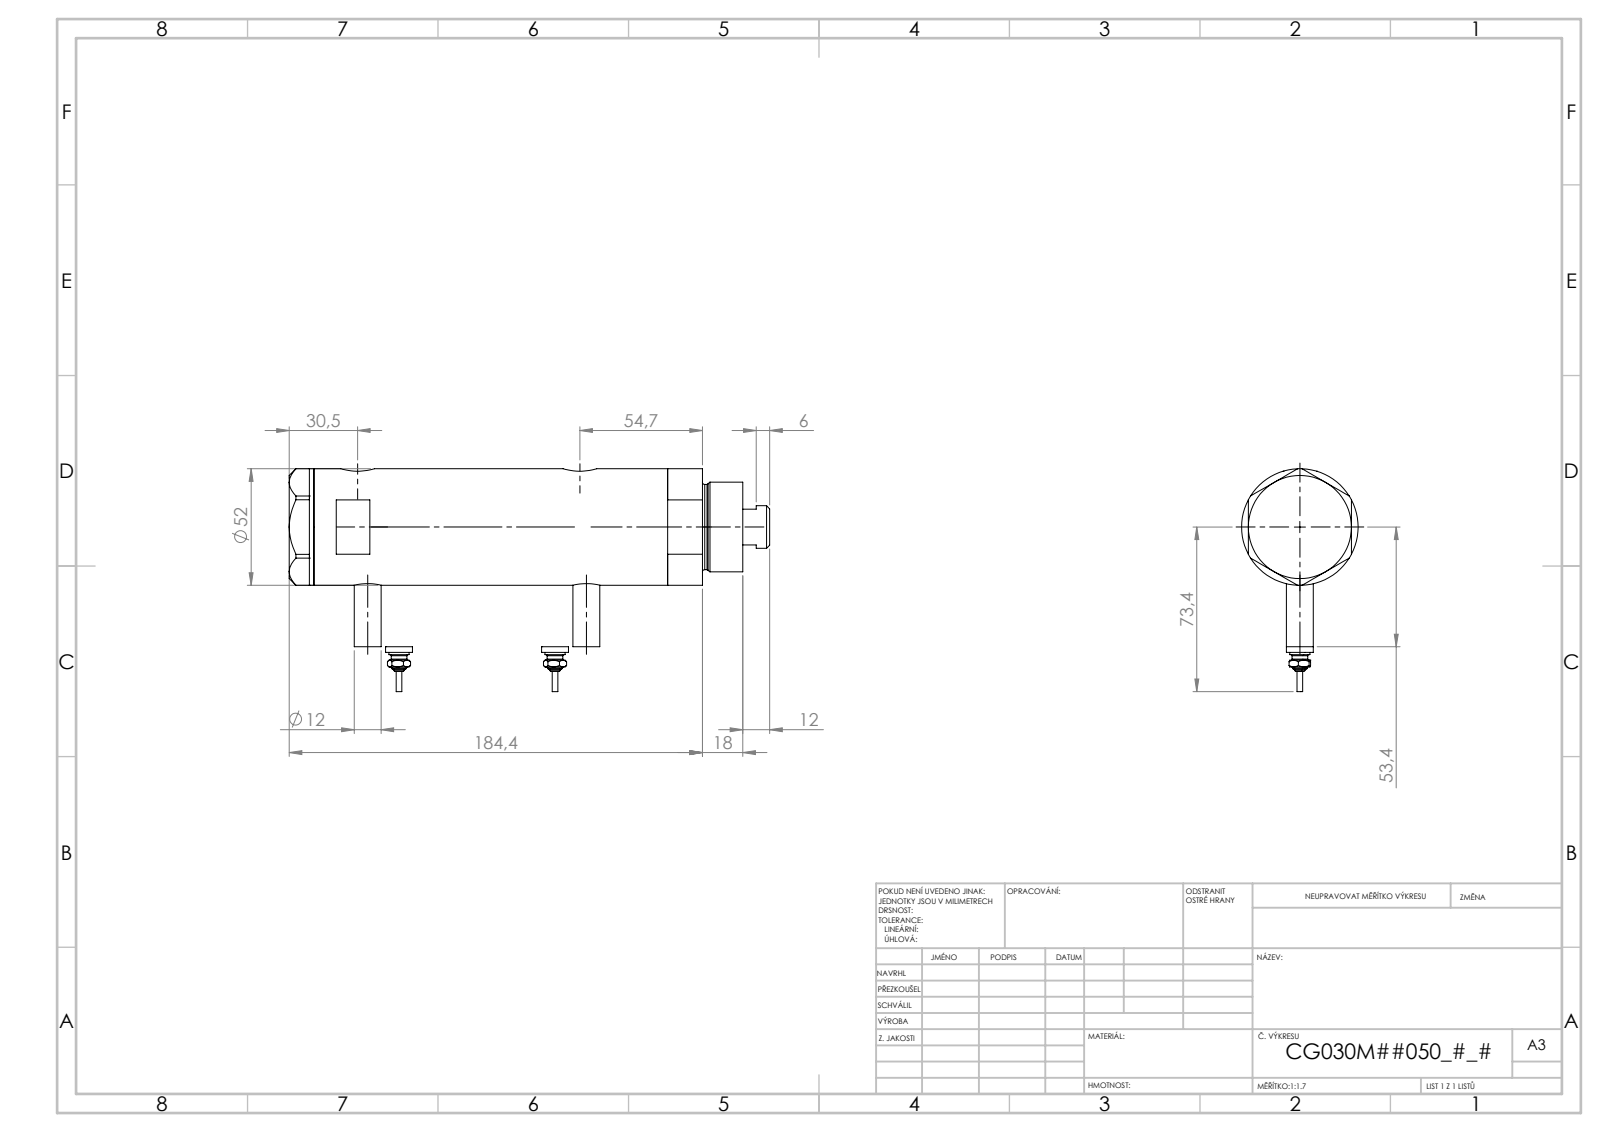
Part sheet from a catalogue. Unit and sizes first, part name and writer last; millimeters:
Units: millimetres
Overall size (bounding box): 199.02 × 84.3 × 52
Round holes (diameter × count): ⌀5 ×2, ⌀9.73 ×2, ⌀12.5 ×2, ⌀15 ×2, ⌀6.5 ×1, ⌀20 ×1, ⌀21.5 ×1, ⌀30 ×1, ⌀33 ×1, ⌀44 ×1
Round bosses / shafts (diameter × count): ⌀12 ×3, ⌀9 ×2, ⌀7 ×2, ⌀4.34 ×2, ⌀2.4 ×2, ⌀52 ×1, ⌀40 ×1, ⌀38 ×1
Main face-to-face distances: 103.54, 23.8, 79.74, 11, 34.8, 114.54, 46, 150.94, 139.94, 116.14
Hole centre spacings: 2.9, 4.5, 76.75, 79.65, 81.25, 84.15, 2.89, 2.91
Volume: 356 926 mm³ · Surface area: 83 058 mm²
Bodies: 6 solids, 246 faces (95 planar, 77 cylindrical, 74 other)
Part name (STEP PRODUCT): V270CG_MIDDLE; V270CG_VC; V270CG_BACK; V270CG_FRONT (+1 more)
STEP written by: SolidWorks 2019 (CONFIG_CONTROL_DESIGN)
